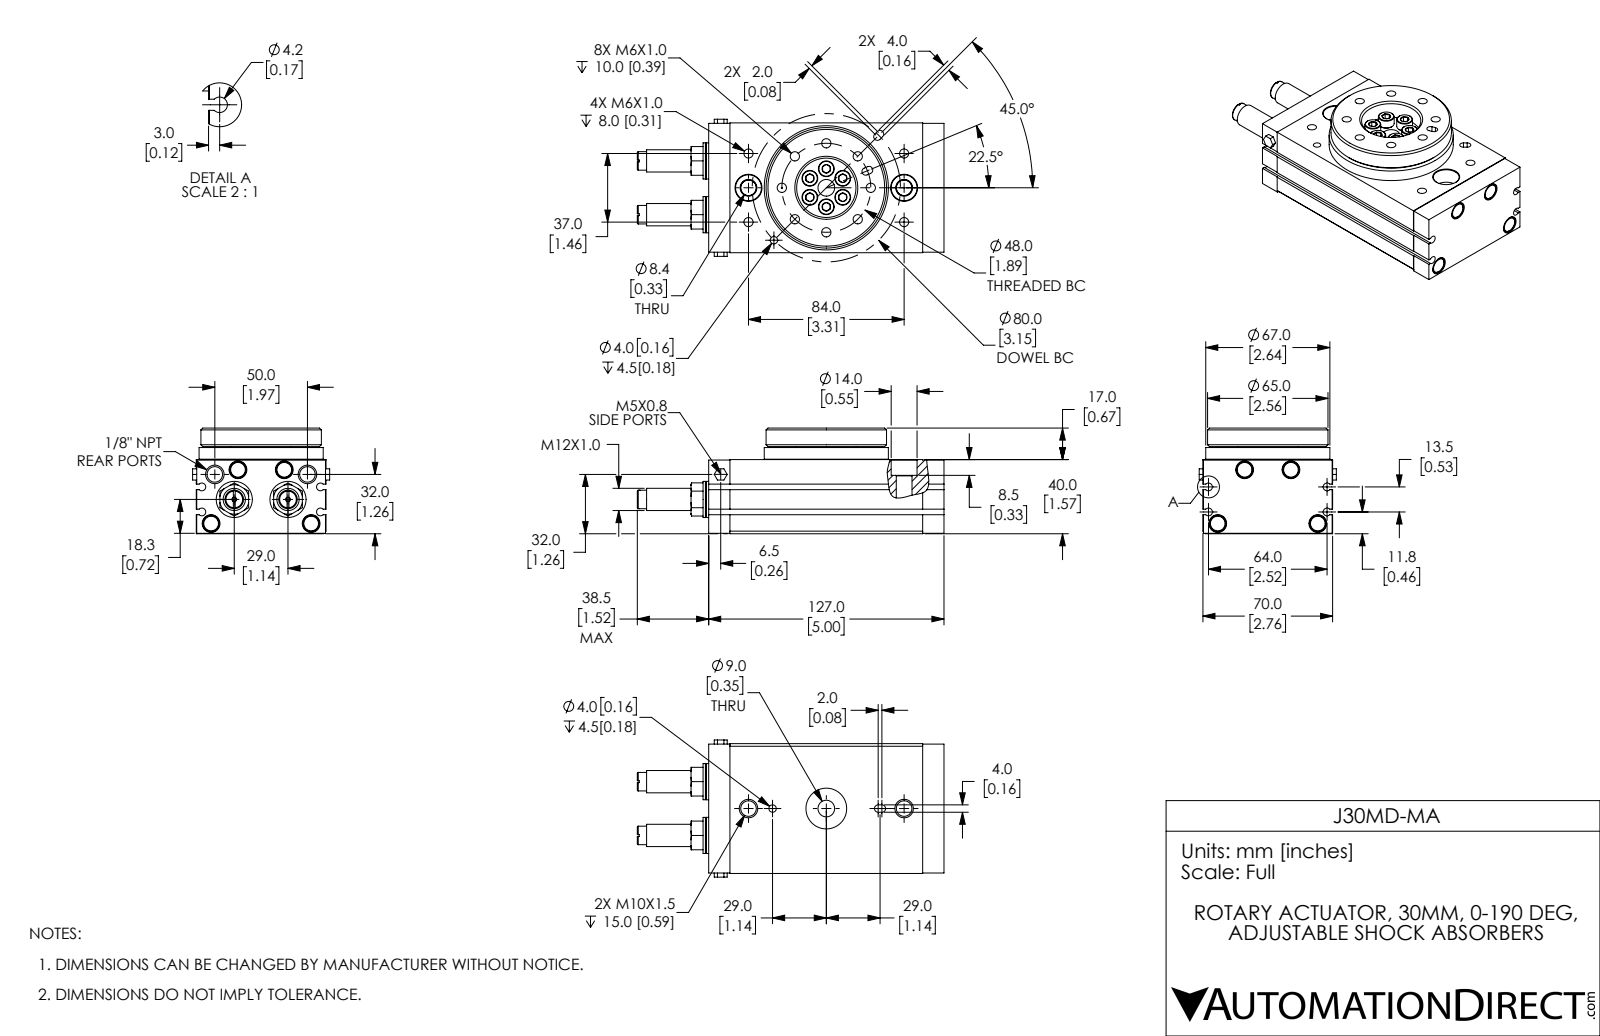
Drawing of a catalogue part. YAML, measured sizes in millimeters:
part_name: "J30MD-MA; J30MD-MA_M5_91290A221; J30MD-MA_table; J30MD-MA_body2"
step_written_by: "SolidWorks 2017 (AUTOMOTIVE_DESIGN)"
units: millimeters
bodies: {solids: 8, faces: 721, planar: 197, cylindrical: 326, other: 198}
overall_size: [165.5, 74, 57]
volume: 390061
surface_area: 64906
round_holes:
  - {diameter: 5, count: 12}
  - {diameter: 9, count: 5}
  - {diameter: 4.92, count: 4}
  - {diameter: 8.38, count: 4}
  - {diameter: 2, count: 2}
  - {diameter: 8.5, count: 2}
  - {diameter: 14, count: 2}
  - {diameter: 22, count: 1}
  - {diameter: 32, count: 1}
  - {diameter: 33, count: 1}
round_bosses_or_shafts:
  - {diameter: 8.5, count: 10}
  - {diameter: 5, count: 6}
  - {diameter: 3.96, count: 6}
  - {diameter: 19.5, count: 2}
  - {diameter: 12, count: 2}
  - {diameter: 10, count: 2}
  - {diameter: 67, count: 1}
  - {diameter: 65, count: 1}
partial_cylinders:
  - {radius: 2, count: 6}
  - {radius: 2.1, count: 4}
face_to_face_distances: [70, 40, 39.75, 7, 47, 6.5, 0.5, 46.5, 10, 10.5]
hole_center_spacings: [18.37, 24, 33.94, 44.35, 10.25, 18.5, 20.86, 25.08]
